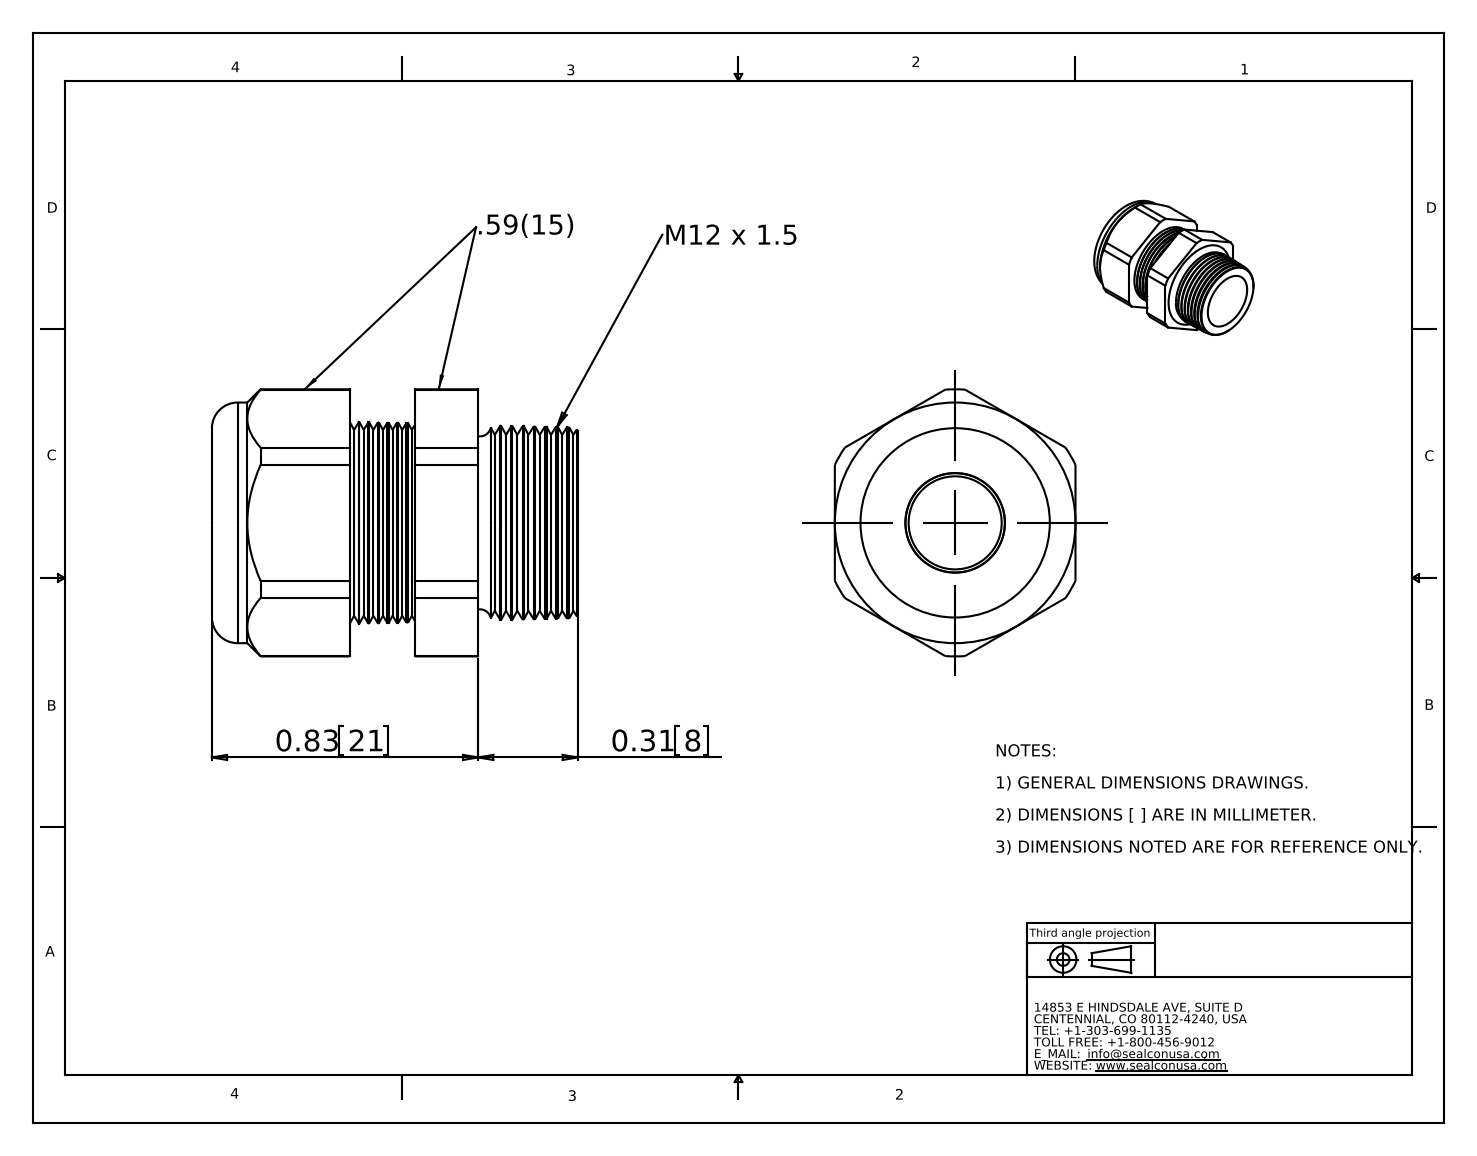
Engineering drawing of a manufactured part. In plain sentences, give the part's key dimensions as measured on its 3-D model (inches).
The part is named "CD12MP-GY". Its 3-D file was written by "SolidWorks 2007 (CONFIG_CONTROL_DESIGN)". It is 2 solids with 144 faces: 20 planar, 20 cylindrical and 104 other. Overall it measures 1.14 by 0.833 by 0.75 inches. Its volume is 0.33 cubic inches and its surface area 5.963 square inches. Round holes: 1 of diameter 0.29, 1 of diameter 0.31. Round bosses or shafts: 1 of diameter 0.75. Partial cylindrical surfaces (rounded edges, fillets, slot ends): 1 of radius 0.416. The main face-to-face distances are 0.75, 0.75, 0.633, 0.429, 0.204, 0.83, 0.401, 0.197, 1.14, 0.711.
